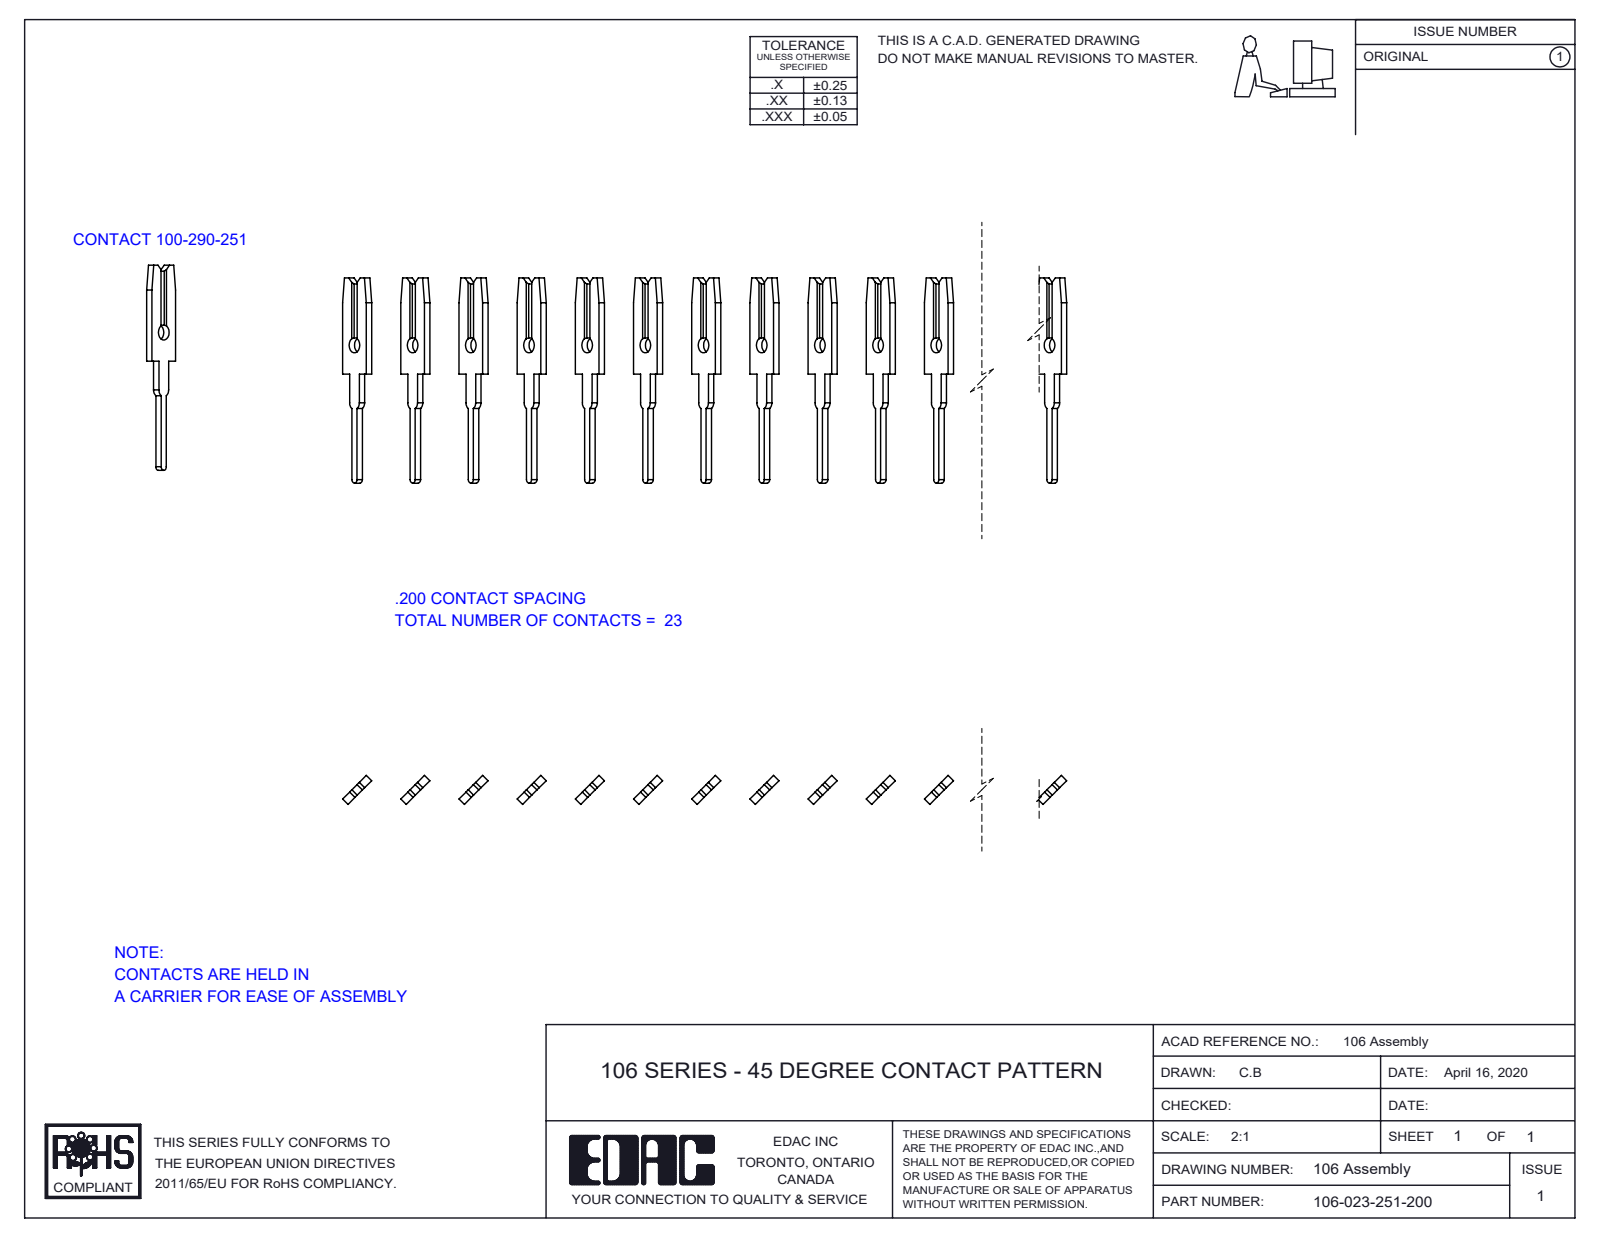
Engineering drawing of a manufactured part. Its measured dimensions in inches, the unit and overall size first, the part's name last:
Units: inches
Overall size (bounding box): 4.5 × 0.705 × 0.1
Round holes (diameter × count): ⌀0.052 ×23
Partial cylindrical surfaces — rounded edges, fillets, slot ends (radius × count): R0.012 ×23, R0.024 ×23
Main face-to-face distances: 0.141, 0.848, 0.283, 0.707, 0.99, 0.566, 1.131, 0.424, 0.424, 1.556
Hole centre spacings: 0.141, 0.283, 0.424, 1.131, 1.556, 0.848, 1.697, 1.839
Volume: 0.026 in³ · Surface area: 3.204 in²
Bodies: 23 solids, 644 faces (506 planar, 138 cylindrical, 0 other)
Part name (STEP PRODUCT): 106-023-251-200; 100-290-001_100-290-251
STEP written by: SolidWorks 2016 (CONFIG_CONTROL_DESIGN)
